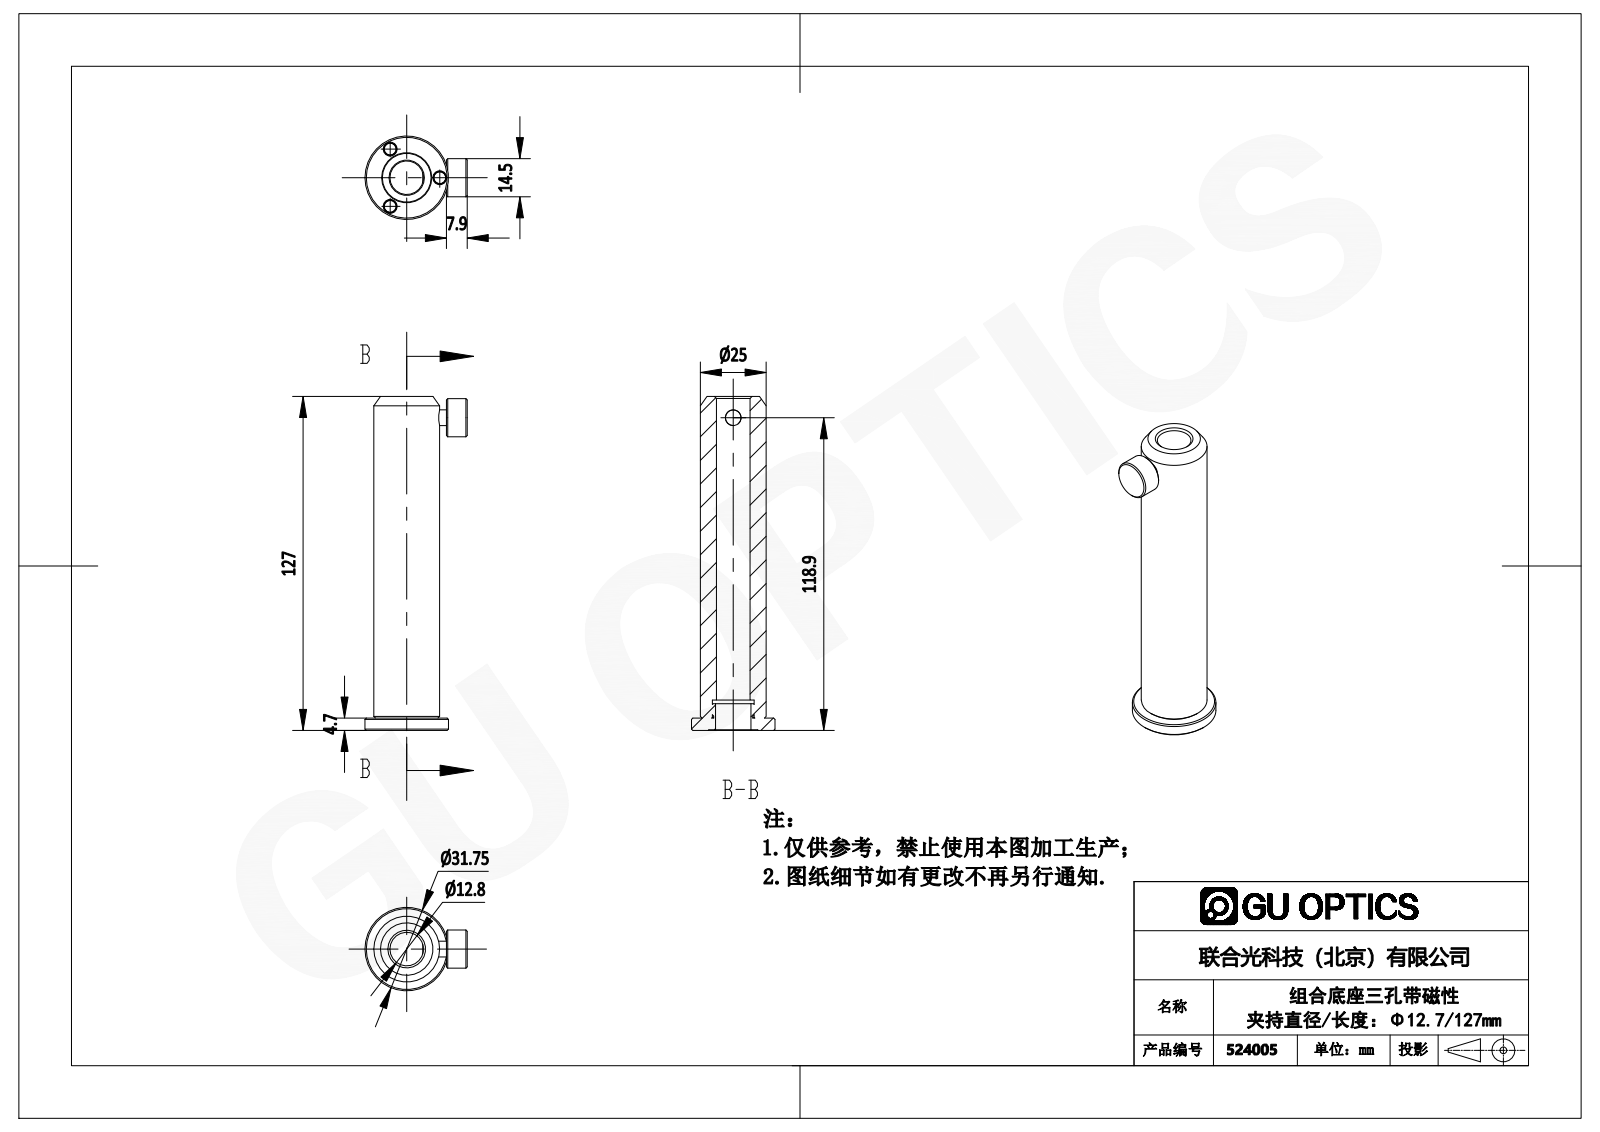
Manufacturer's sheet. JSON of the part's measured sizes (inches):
{"part_name": "524005", "step_written_by": "SolidWorks 2016 (AUTOMOTIVE_DESIGN)", "units": "inches", "bodies": {"solids": 5, "faces": 90, "planar": 19, "cylindrical": 31, "other": 40}, "overall_size": [5, 1.531, 1.25], "volume_in3": 2.942, "surface_area_in2": 28.14, "round_holes": [[0.19, 3], [0.236, 1], [0.503, 1], [0.53, 1], [0.625, 1]], "round_bosses_or_shafts": [[0.187, 3], [1.25, 1], [0.985, 1], [0.585, 1], [0.571, 1]], "partial_cylinders_radius": [[0.313, 1]], "face_to_face_distances": [0.185, 5, 4.815, 0.175, 4.99, 0.311, 0.455, 0.445, 0.27, 4.545], "hole_center_spacings": [0.857, 0.495, 0.495]}
